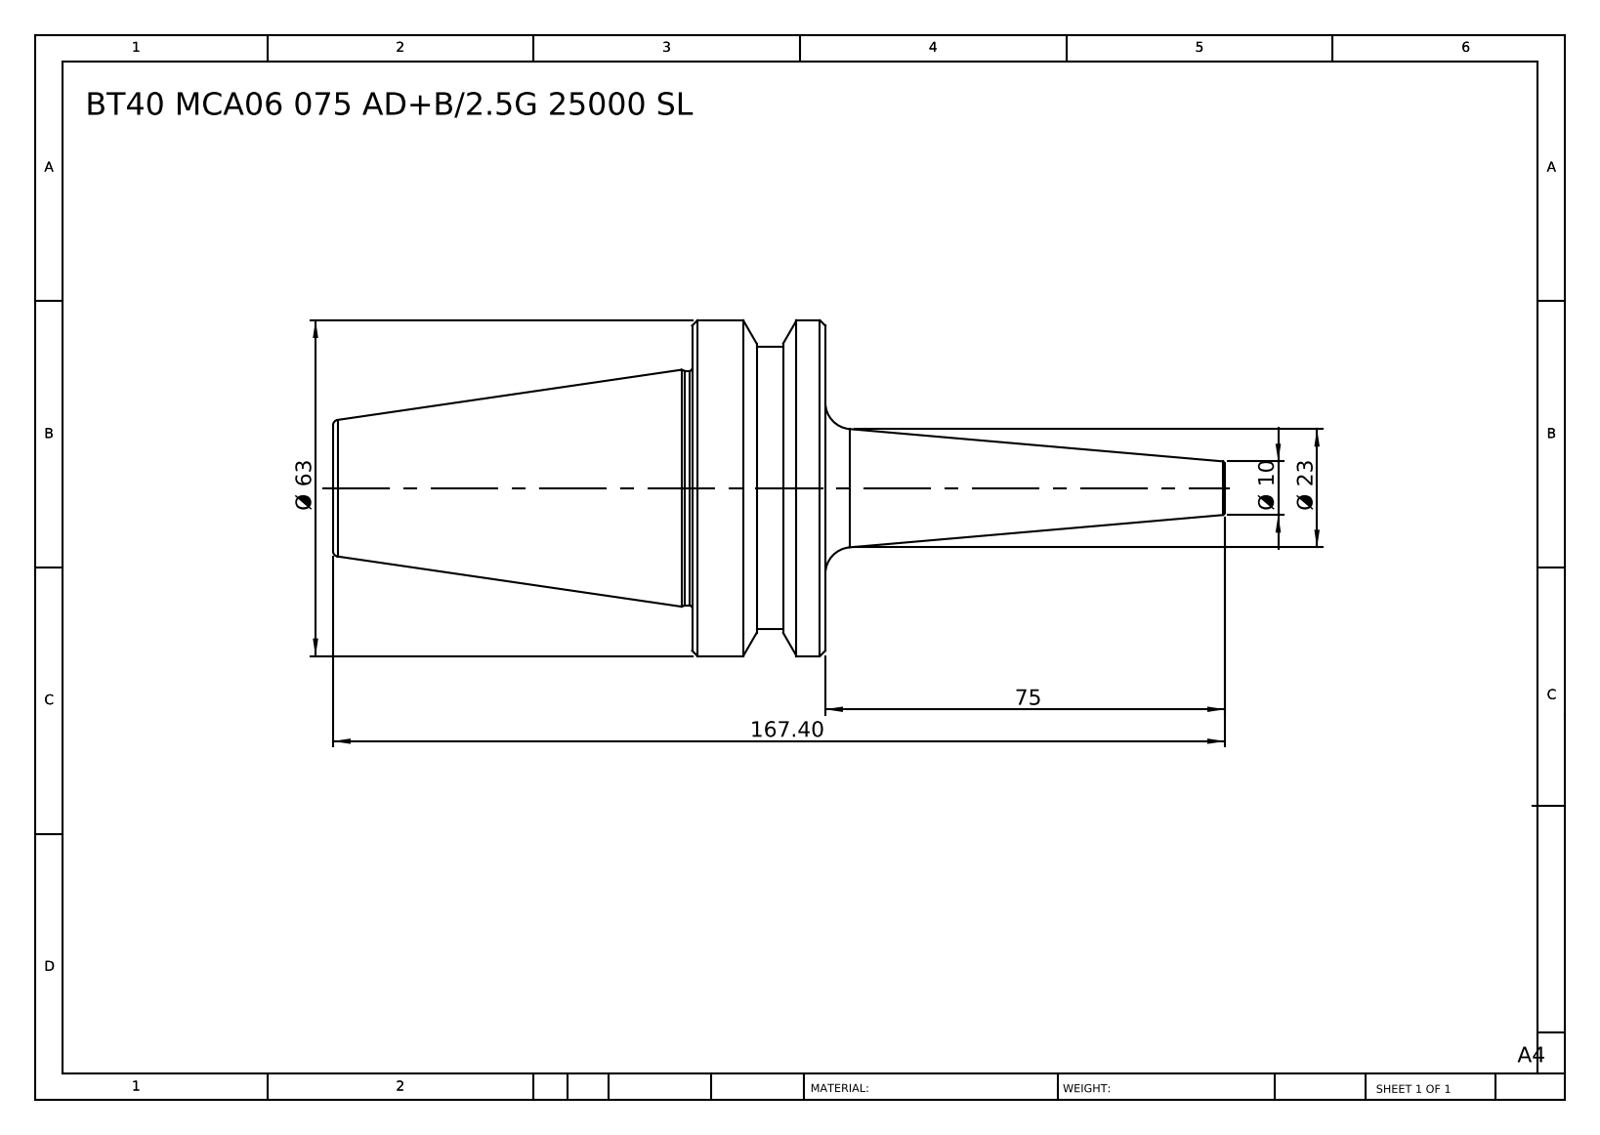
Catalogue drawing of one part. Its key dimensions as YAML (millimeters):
part_name: "BT40-MCA06 075 AD+B-2.5G 25000 SL"
step_written_by: "SolidWorks 2014 (CONFIG_CONTROL_DESIGN)"
units: millimeters
bodies: {solids: 1, faces: 38, planar: 6, cylindrical: 8, other: 24}
overall_size: [167.4, 63, 63]
volume: 155553
surface_area: 21776
round_bosses_or_shafts:
  - {diameter: 63, count: 1}
  - {diameter: 53, count: 1}
  - {diameter: 44, count: 1}
face_to_face_distances: [25, 92.4, 67.4, 12.9, 12.1, 79.5, 7.9, 5, 17.1, 84.5]
